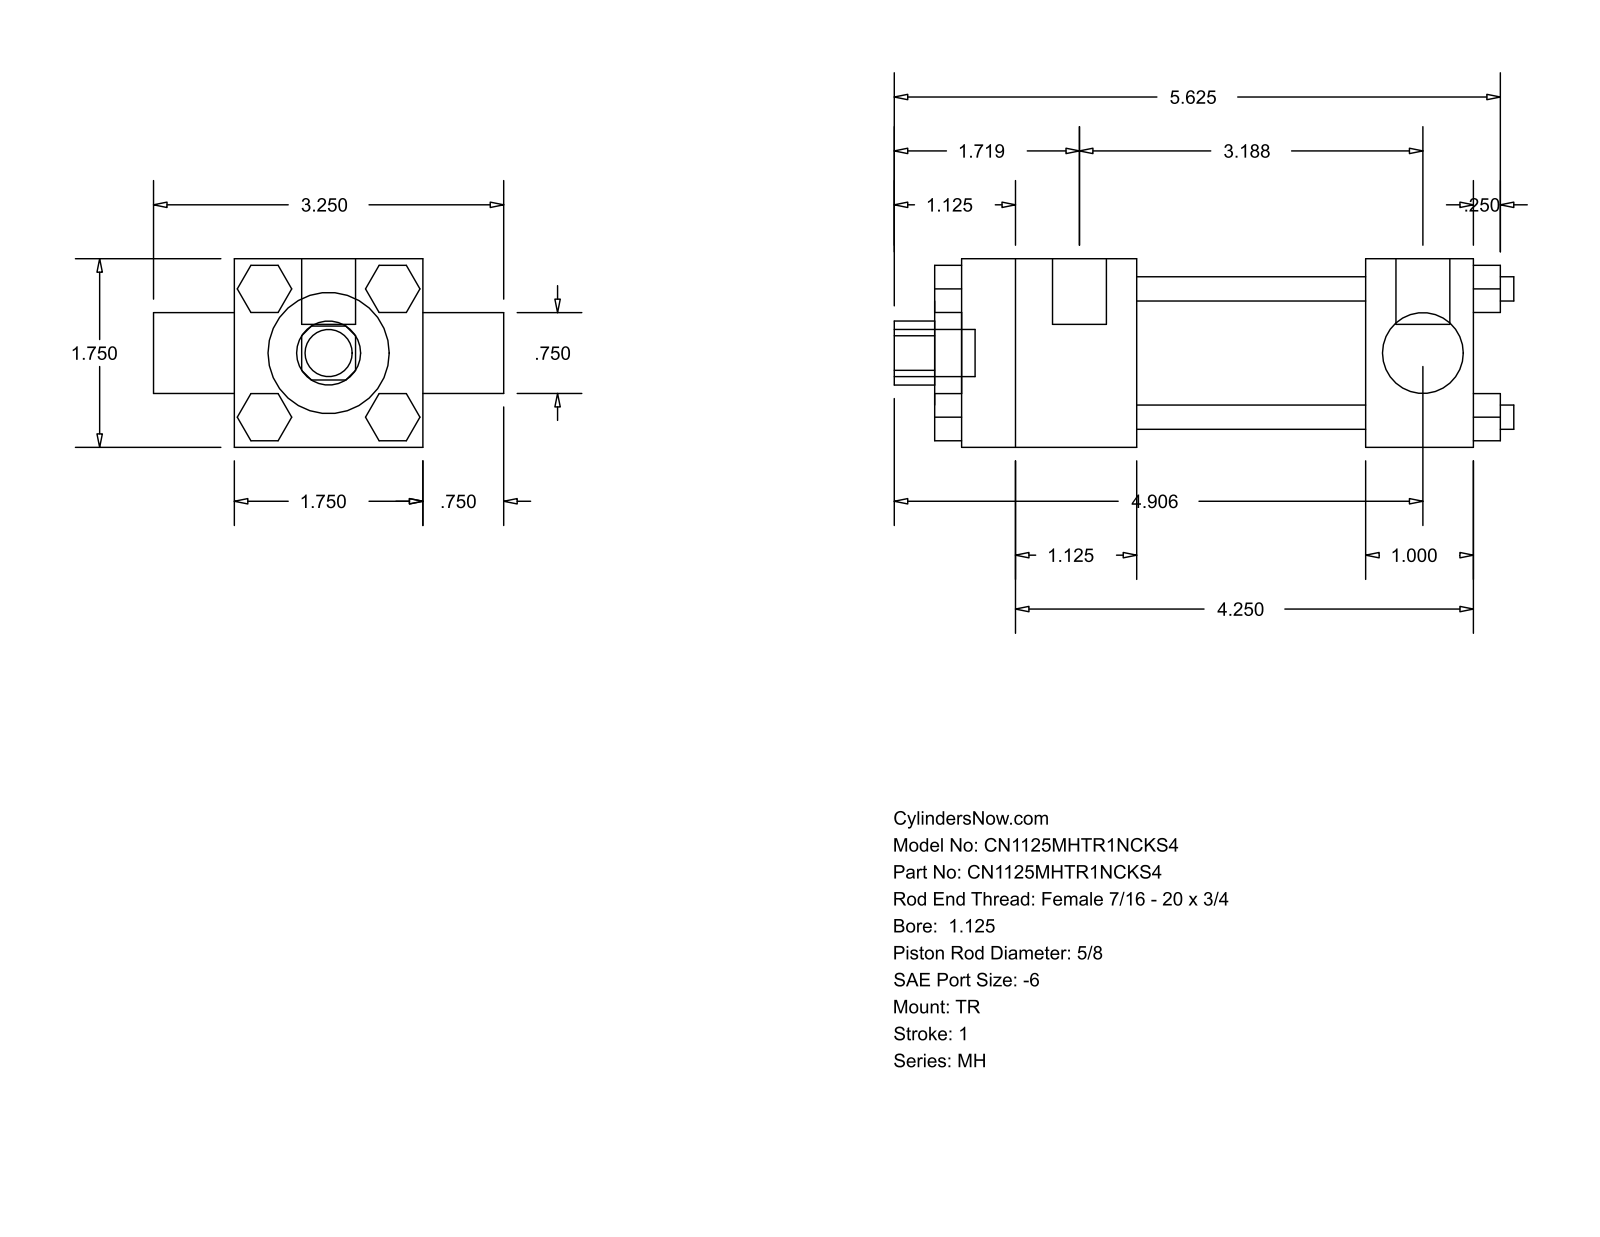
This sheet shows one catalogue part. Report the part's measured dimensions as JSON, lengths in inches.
{"part_name": "MH_TR__0112_0.625", "step_written_by": "GSSL Pune (CONFIG_CONTROL_DESIGN)", "units": "inches", "bodies": {"solids": 0, "faces": 120, "planar": 92, "cylindrical": 28, "other": 0}, "overall_size": [5.75, 3.25, 1.75], "round_holes": [[0.625, 1], [0.75, 1], [1.125, 1], [1.375, 1]], "round_bosses_or_shafts": [[0.225, 4], [0.219, 3], [0.5, 2], [0.437, 1]], "partial_cylinders_radius": [[0.297, 1]], "face_to_face_distances": [1.75, 5, 0.25, 0.437, 2.125, 3.125, 1, 1.625, 3.75, 4.75]}
